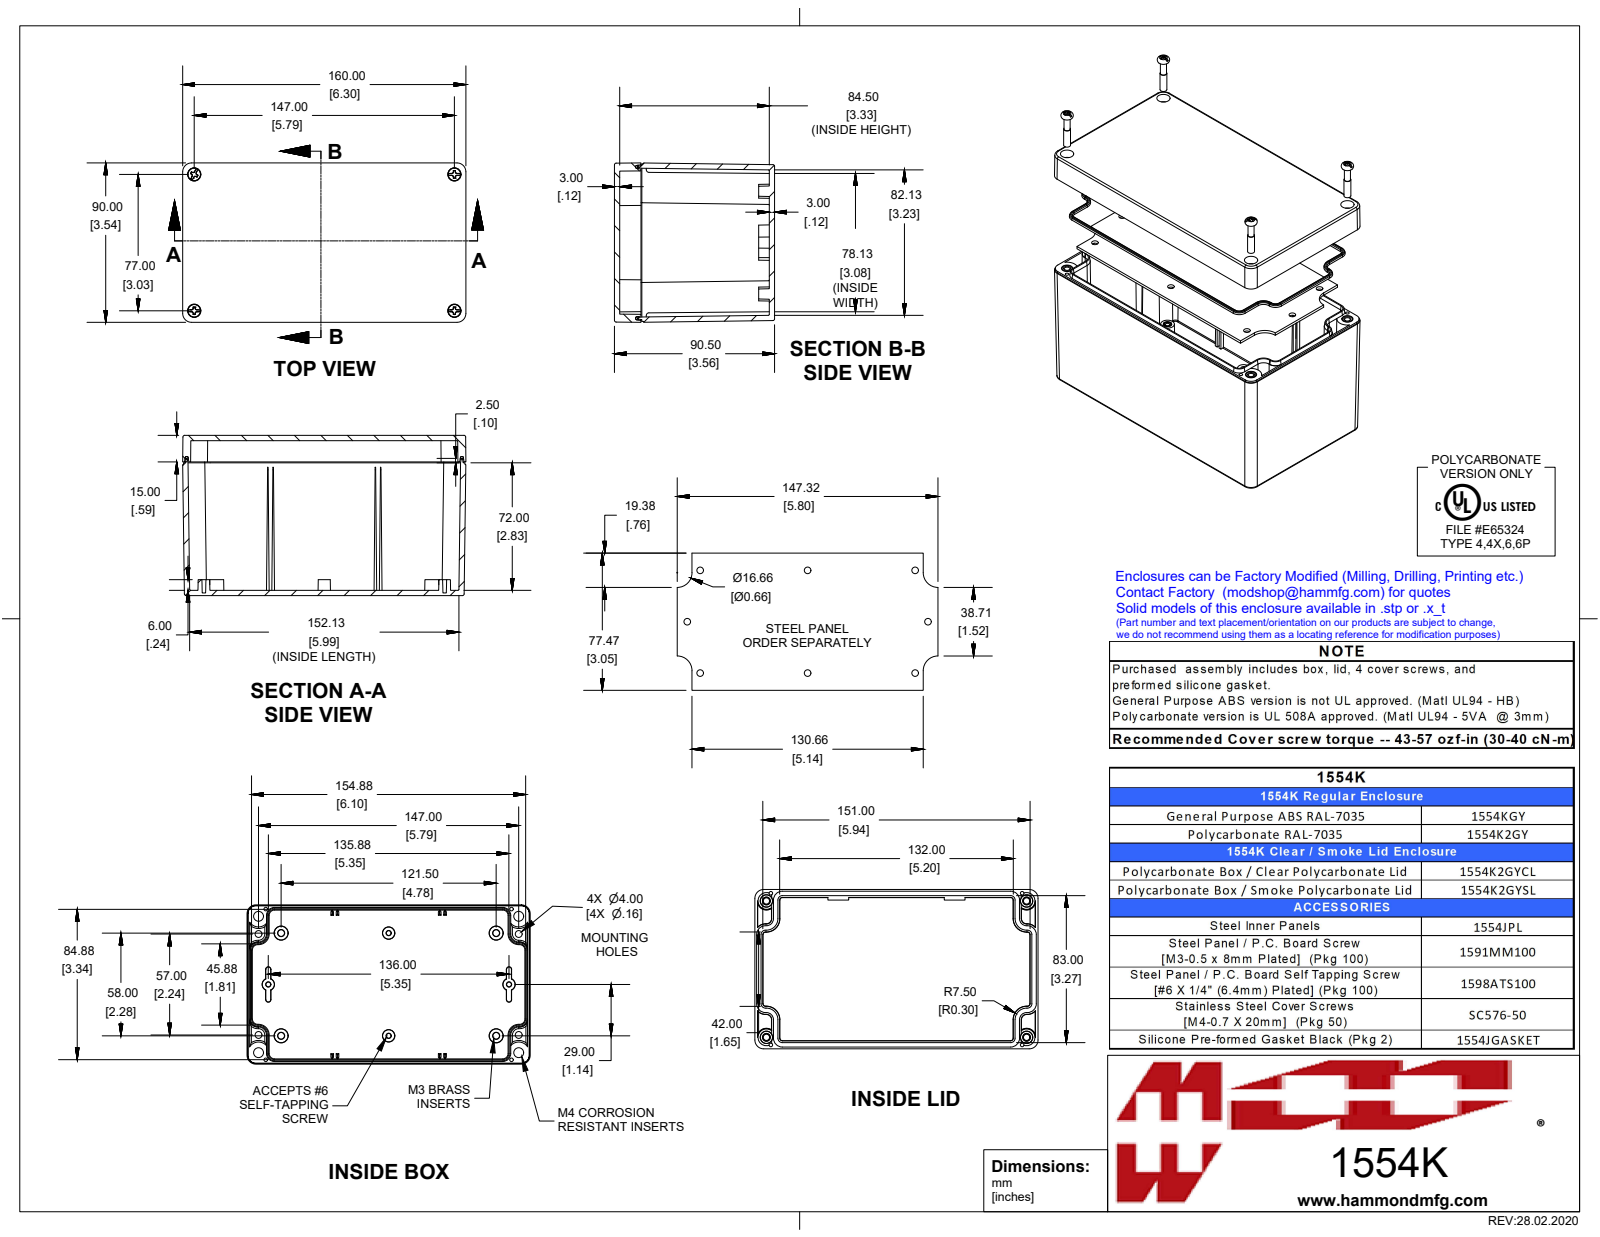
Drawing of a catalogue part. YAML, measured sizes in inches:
part_name: "1554K2GY"
step_written_by: "SolidWorks 2019 (AUTOMOTIVE_DESIGN)"
units: inches
bodies: {solids: 15, faces: 1318, planar: 374, cylindrical: 322, other: 622}
overall_size: [6.299, 3.563, 3.543]
volume: 14.72
surface_area: 267.7
round_holes:
  - {diameter: 0.079, count: 8}
  - {diameter: 0.097, count: 4}
  - {diameter: 0.128, count: 4}
  - {diameter: 0.138, count: 4}
  - {diameter: 0.276, count: 4}
round_bosses_or_shafts:
  - {diameter: 0.25, count: 4}
  - {diameter: 0.218, count: 4}
  - {diameter: 0.21, count: 4}
  - {diameter: 0.19, count: 4}
  - {diameter: 0.154, count: 4}
  - {diameter: 0.153, count: 4}
  - {diameter: 0.15, count: 4}
  - {diameter: 0.135, count: 4}
partial_cylinders:
  - {radius: 0.02, count: 24}
  - {radius: 0.039, count: 8}
  - {radius: 0.197, count: 8}
  - {radius: 0.187, count: 4}
  - {radius: 0.059, count: 2}
face_to_face_distances: [0.118, 3.445, 3.563, 3.327, 0.059, 0.492, 0.177, 0.374, 0.433, 0.023]
hole_center_spacings: [0.197, 0.626, 0.678, 2.704, 2.857, 3.204, 5.215, 5.299]
